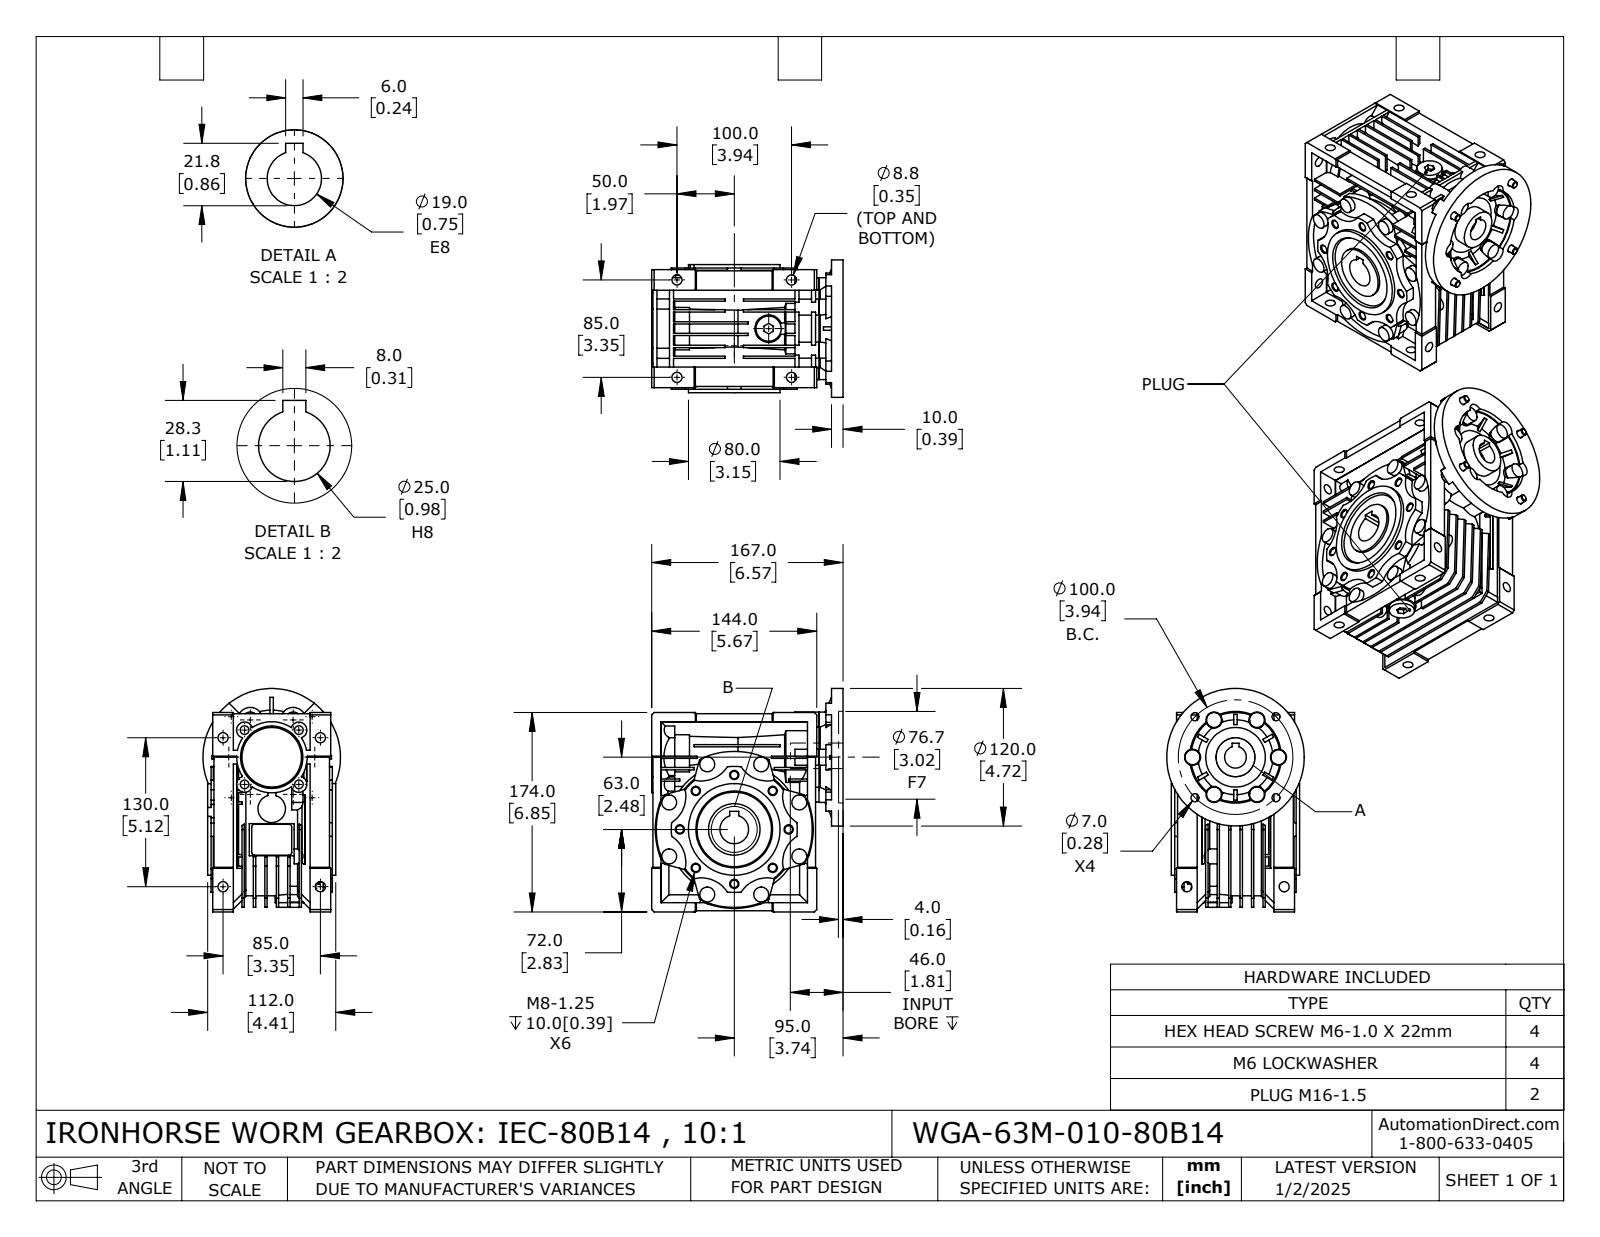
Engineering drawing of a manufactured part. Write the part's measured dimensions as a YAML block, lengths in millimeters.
part_name: "WGA-63M-010-80B14"
step_written_by: "SolidWorks 2024 (CONFIG_CONTROL_DESIGN)"
units: millimeters
bodies: {solids: 16, faces: 1442, planar: 853, cylindrical: 413, other: 176}
overall_size: [195, 172.5, 120]
volume: 1847000
surface_area: 350234
round_holes:
  - {diameter: 6.65, count: 8}
  - {diameter: 8.78, count: 8}
  - {diameter: 6.1, count: 4}
  - {diameter: 7, count: 4}
  - {diameter: 7.56, count: 4}
  - {diameter: 14.5, count: 2}
  - {diameter: 19, count: 1}
  - {diameter: 20, count: 1}
  - {diameter: 25, count: 1}
  - {diameter: 34, count: 1}
  - {diameter: 37, count: 1}
  - {diameter: 45, count: 1}
round_bosses_or_shafts:
  - {diameter: 13, count: 14}
  - {diameter: 14, count: 6}
  - {diameter: 12.2, count: 4}
  - {diameter: 6, count: 4}
  - {diameter: 24, count: 3}
  - {diameter: 22, count: 2}
  - {diameter: 15.8, count: 2}
  - {diameter: 13.7, count: 2}
partial_cylinders:
  - {radius: 7, count: 10}
  - {radius: 27, count: 8}
  - {radius: 6.98, count: 6}
  - {radius: 11, count: 6}
  - {radius: 2.5, count: 4}
  - {radius: 8.35, count: 1}
  - {radius: 29.5, count: 1}
  - {radius: 30.5, count: 1}
face_to_face_distances: [10, 8, 20, 2, 30, 18, 12, 7, 40, 1]
hole_center_spacings: [36.36, 47.5, 60.19, 67.18, 87.77, 16.5, 33.5, 47.38]
